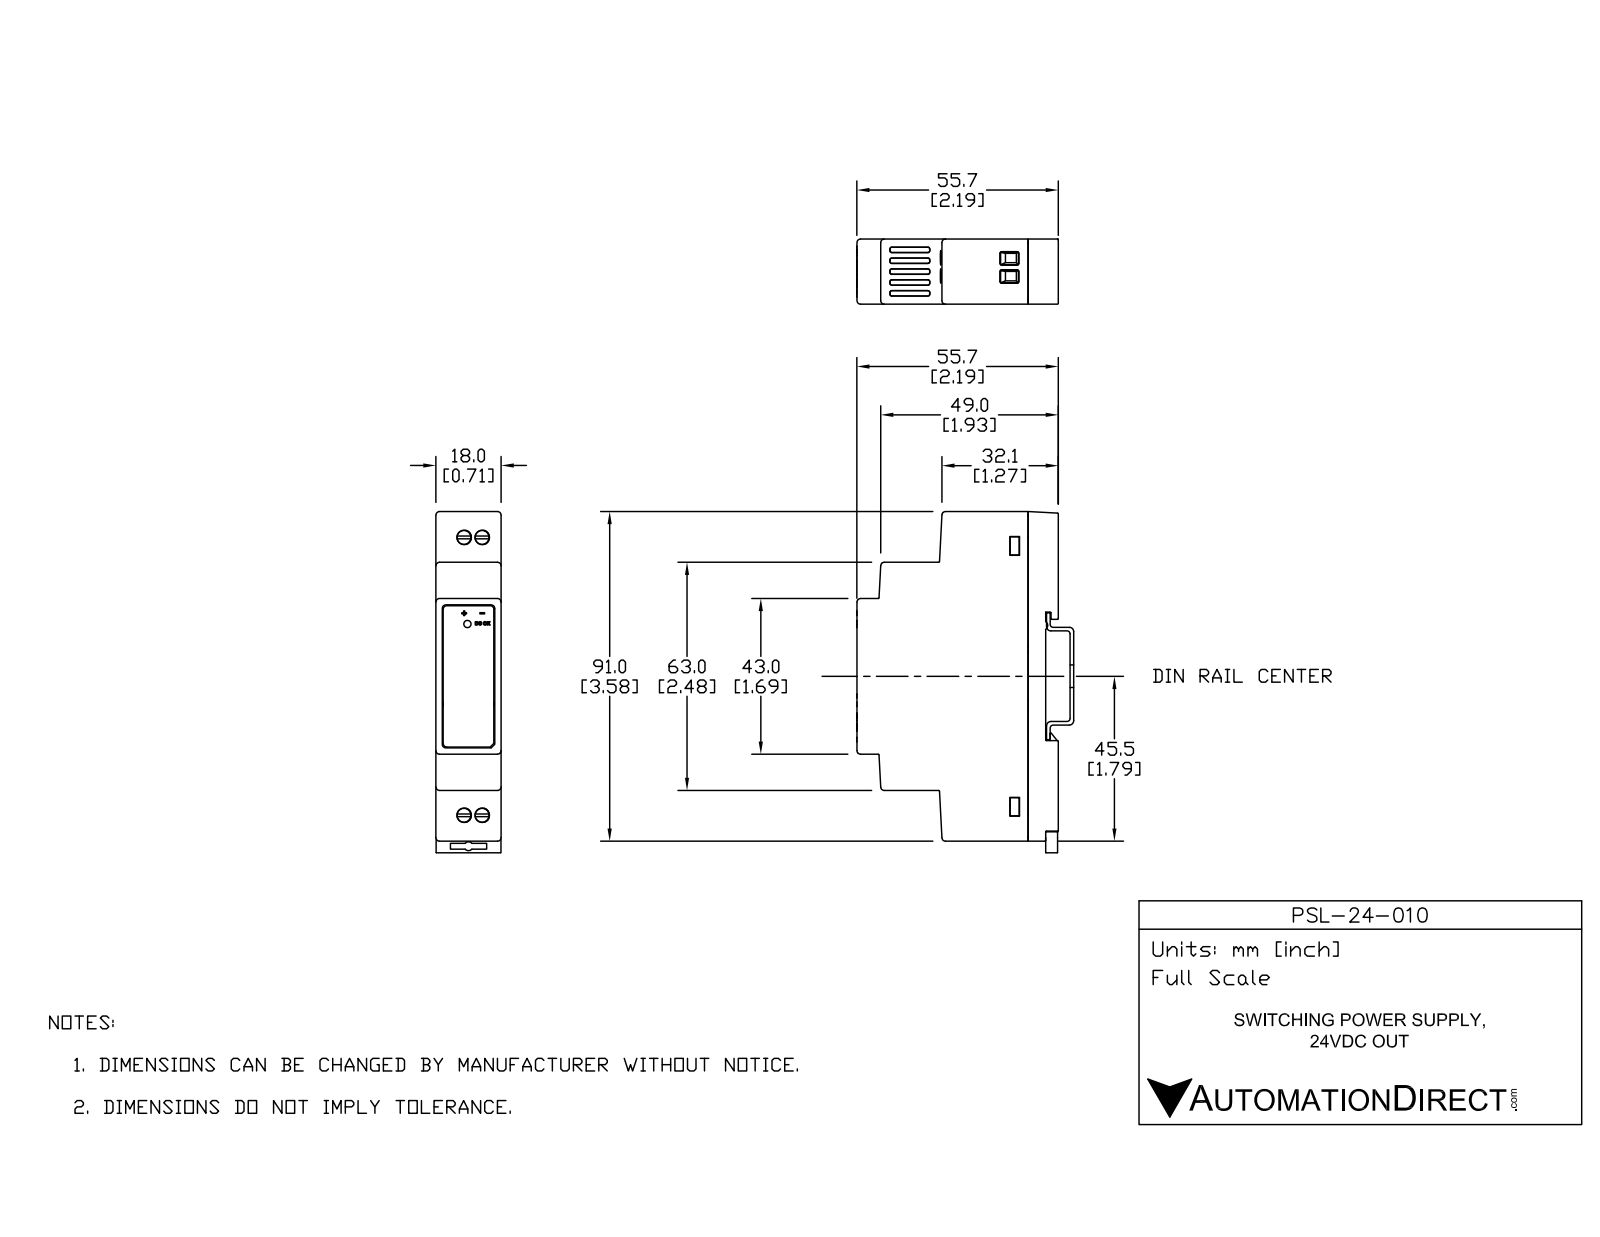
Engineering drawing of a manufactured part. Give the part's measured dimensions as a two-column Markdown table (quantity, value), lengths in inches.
| quantity | value |
| --- | --- |
| part name | PSL-24-010 |
| STEP written by | SolidWorks 2017 (AUTOMOTIVE_DESIGN) |
| units | inches |
| bodies | 10 solids, 1020 faces (531 planar, 351 cylindrical, 138 other) |
| overall size | 3.709 × 2.189 × 0.709 |
| volume | 1.375 in³ |
| surface area | 49.72 in² |
| round holes (diameter × count) | 0.103 × 4, 0.157 × 4, 0.159 × 4, 0.118 × 1 |
| round bosses / shafts (diameter × count) | 0.151 × 4 |
| partial cylindrical surfaces (radius × count) | 0.004 × 100, 0.008 × 87, 0.02 × 58, 0.039 × 35, 0.031 × 8, 0.059 × 6, 0.122 × 2, 0.048 × 1 |
| main face-to-face distances | 0.709, 0.051, 0.228, 0.177, 0.063, 0.165, 0.114, 1.878, 0.071, 1.972 |
| hole center spacings | 3.02, 3.026, 0.197, 0.195, 0.199, 0.942, 2.079, 2.085 |
